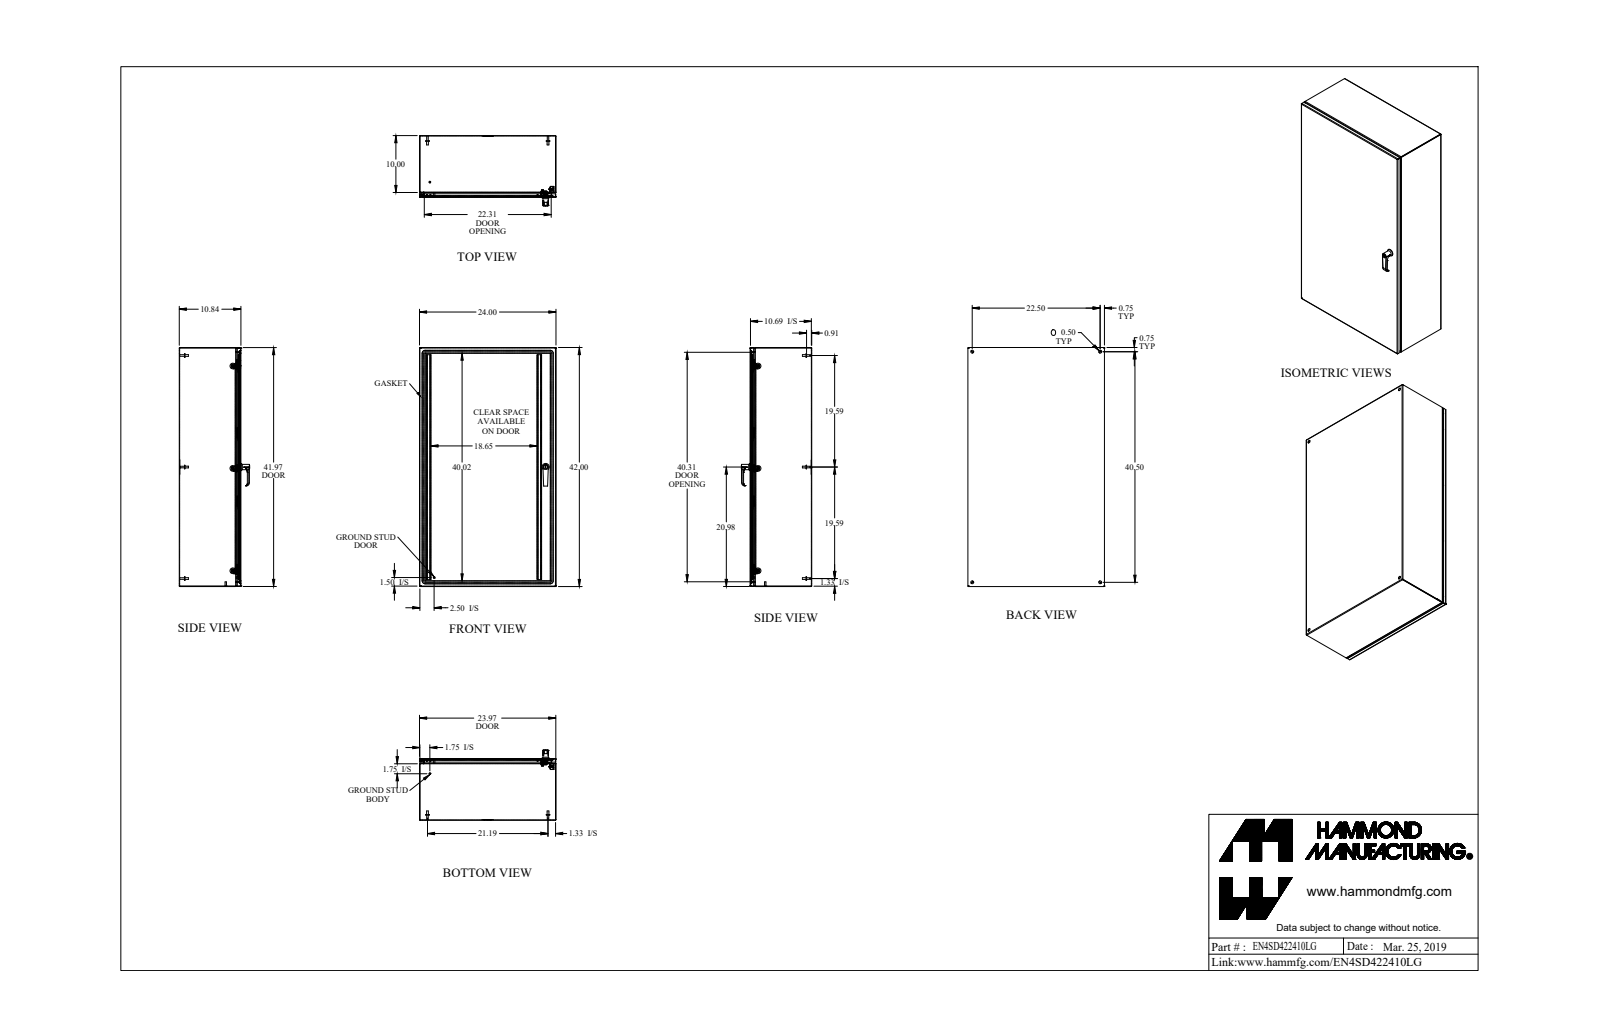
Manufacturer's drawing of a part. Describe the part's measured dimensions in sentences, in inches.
The part is named "EN4SD422410LG". Its 3-D file was written by "SolidWorks 2019 (AUTOMOTIVE_DESIGN)". It is 53 solids with 1457 faces: 632 planar, 538 cylindrical and 287 other. Overall it measures 42 by 24 by 12.367 inches. Its volume is 285.8 cubic inches and its surface area 7 924 square inches. Round holes: 6 of diameter 0.176, 4 of diameter 0.5, 3 of diameter 0.196, 3 of diameter 0.25, 3 of diameter 0.265, 3 of diameter 0.413, 2 of diameter 0.256, 2 of diameter 0.313, 2 of diameter 0.394, 1 of diameter 0.172, 1 of diameter 0.24, 1 of diameter 0.242. Round bosses or shafts: 7 of diameter 0.25, 6 of diameter 0.375, 6 of diameter 0.313, 6 of diameter 0.27, 6 of diameter 0.156, 4 of diameter 0.625, 3 of diameter 1, 2 of diameter 0.63. Partial cylindrical surfaces (rounded edges, fillets, slot ends): 20 of radius 0.036, 20 of radius 0.108, 15 of radius 0.03, 12 of radius 0.043, 12 of radius 0.081, 8 of radius 0.006, 8 of radius 0.04, 8 of radius 0.062. The main face-to-face distances are 0.072, 10.765, 10.693, 10.837, 23.928, 41.928, 23.856, 24, 41.856, 42. The hole center spacings are 0.786, 17.982, 18, 21.061, 22.5, 35.969, 40.5, 46.33.
